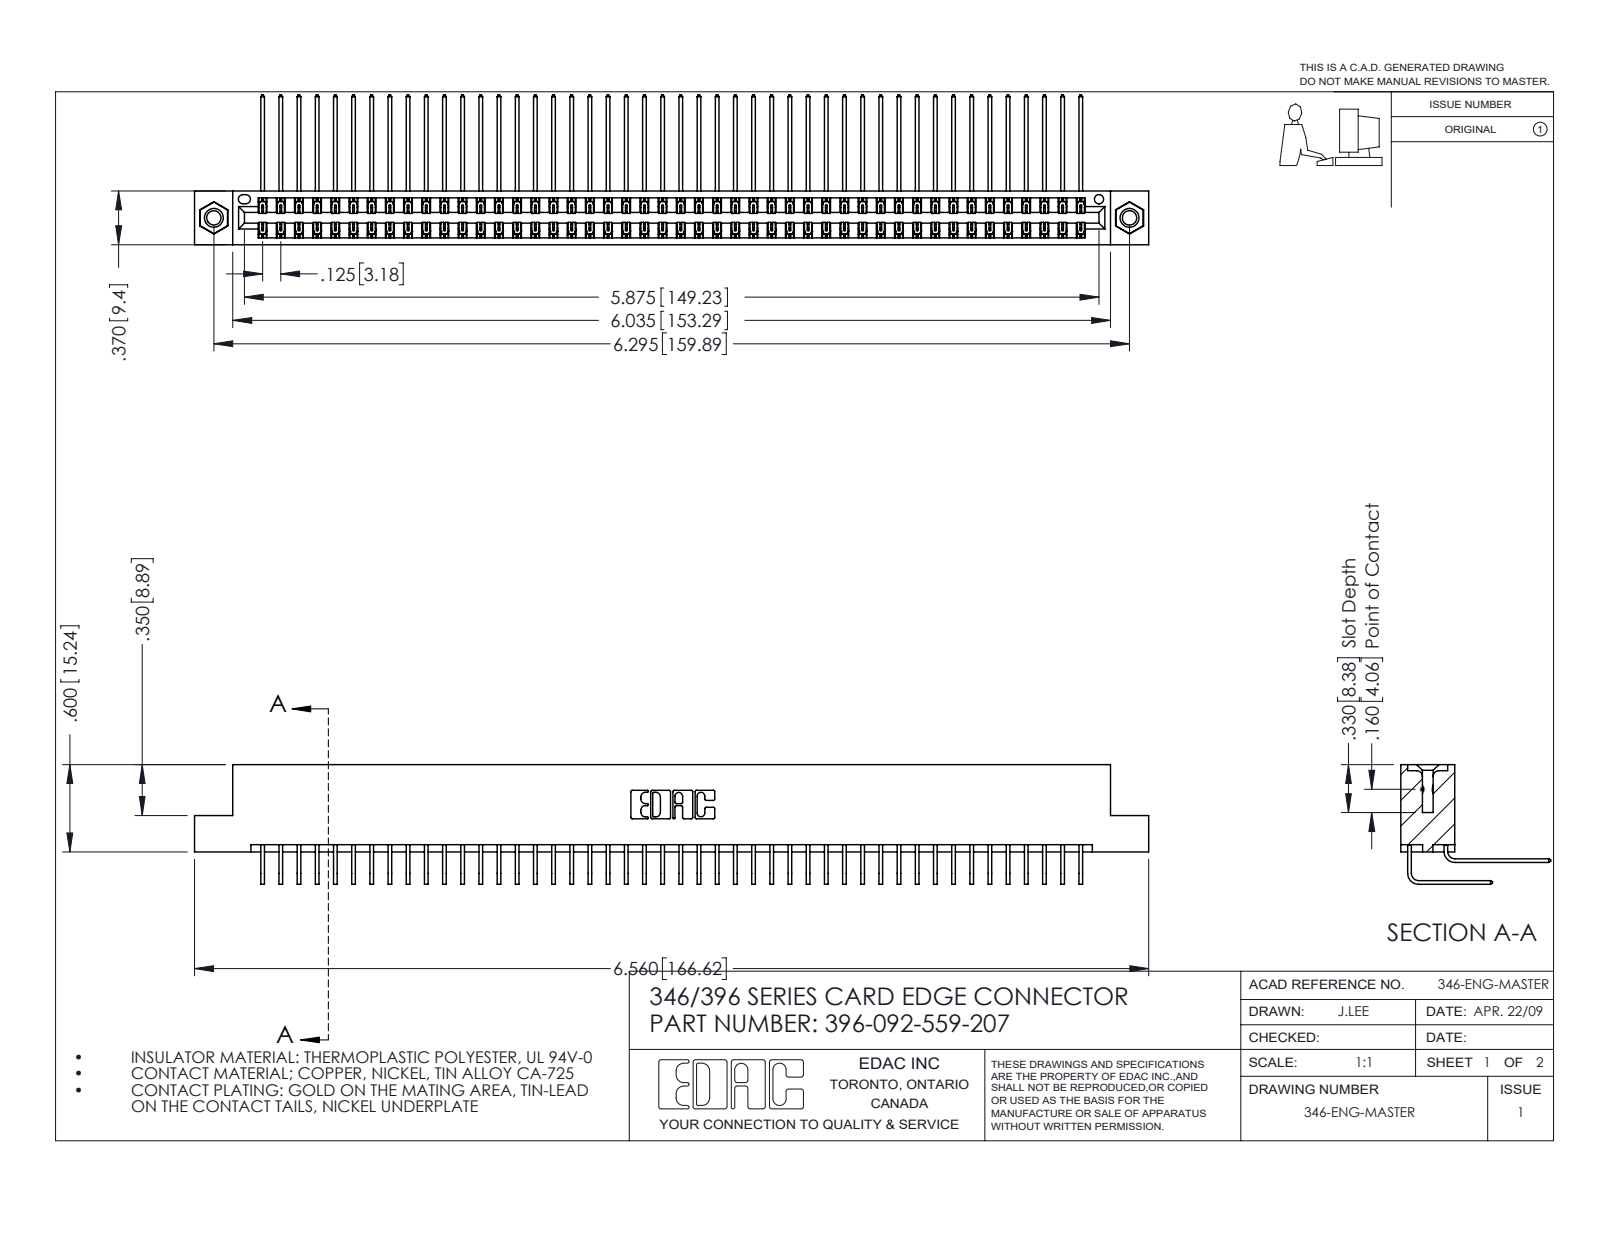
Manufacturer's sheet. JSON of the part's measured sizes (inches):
{"part_name": "396-092-559-207; 345-292-001_559 Tail - 2; 346 Part_Flush Mounting Lugs - 0.156 Dia-TI; 345-250-001_345-250-005-103 (+1 more)", "step_written_by": "SolidWorks 2016 (CONFIG_CONTROL_DESIGN)", "units": "inches", "bodies": {"solids": 95, "faces": 5150, "planar": 3512, "cylindrical": 1622, "other": 16}, "overall_size": [6.56, 1.03, 0.823], "volume_in3": 1.025, "surface_area_in2": 39.88, "round_holes": [[0.098, 2], [0.125, 2], [0.156, 2], [0.064, 1]], "round_bosses_or_shafts": [[0.155, 2]], "partial_cylinders_radius": [[0.006, 138], [0.01, 22], [0.007, 6], [0.031, 6], [0.026, 3], [0.014, 2], [0.022, 2], [0.024, 2]], "face_to_face_distances": [0.048, 0.322, 0.025, 0.37, 0.25, 0.072, 0.298, 0.275, 0.148, 0.222], "hole_center_spacings": [0.246, 6.086, 6.295]}
